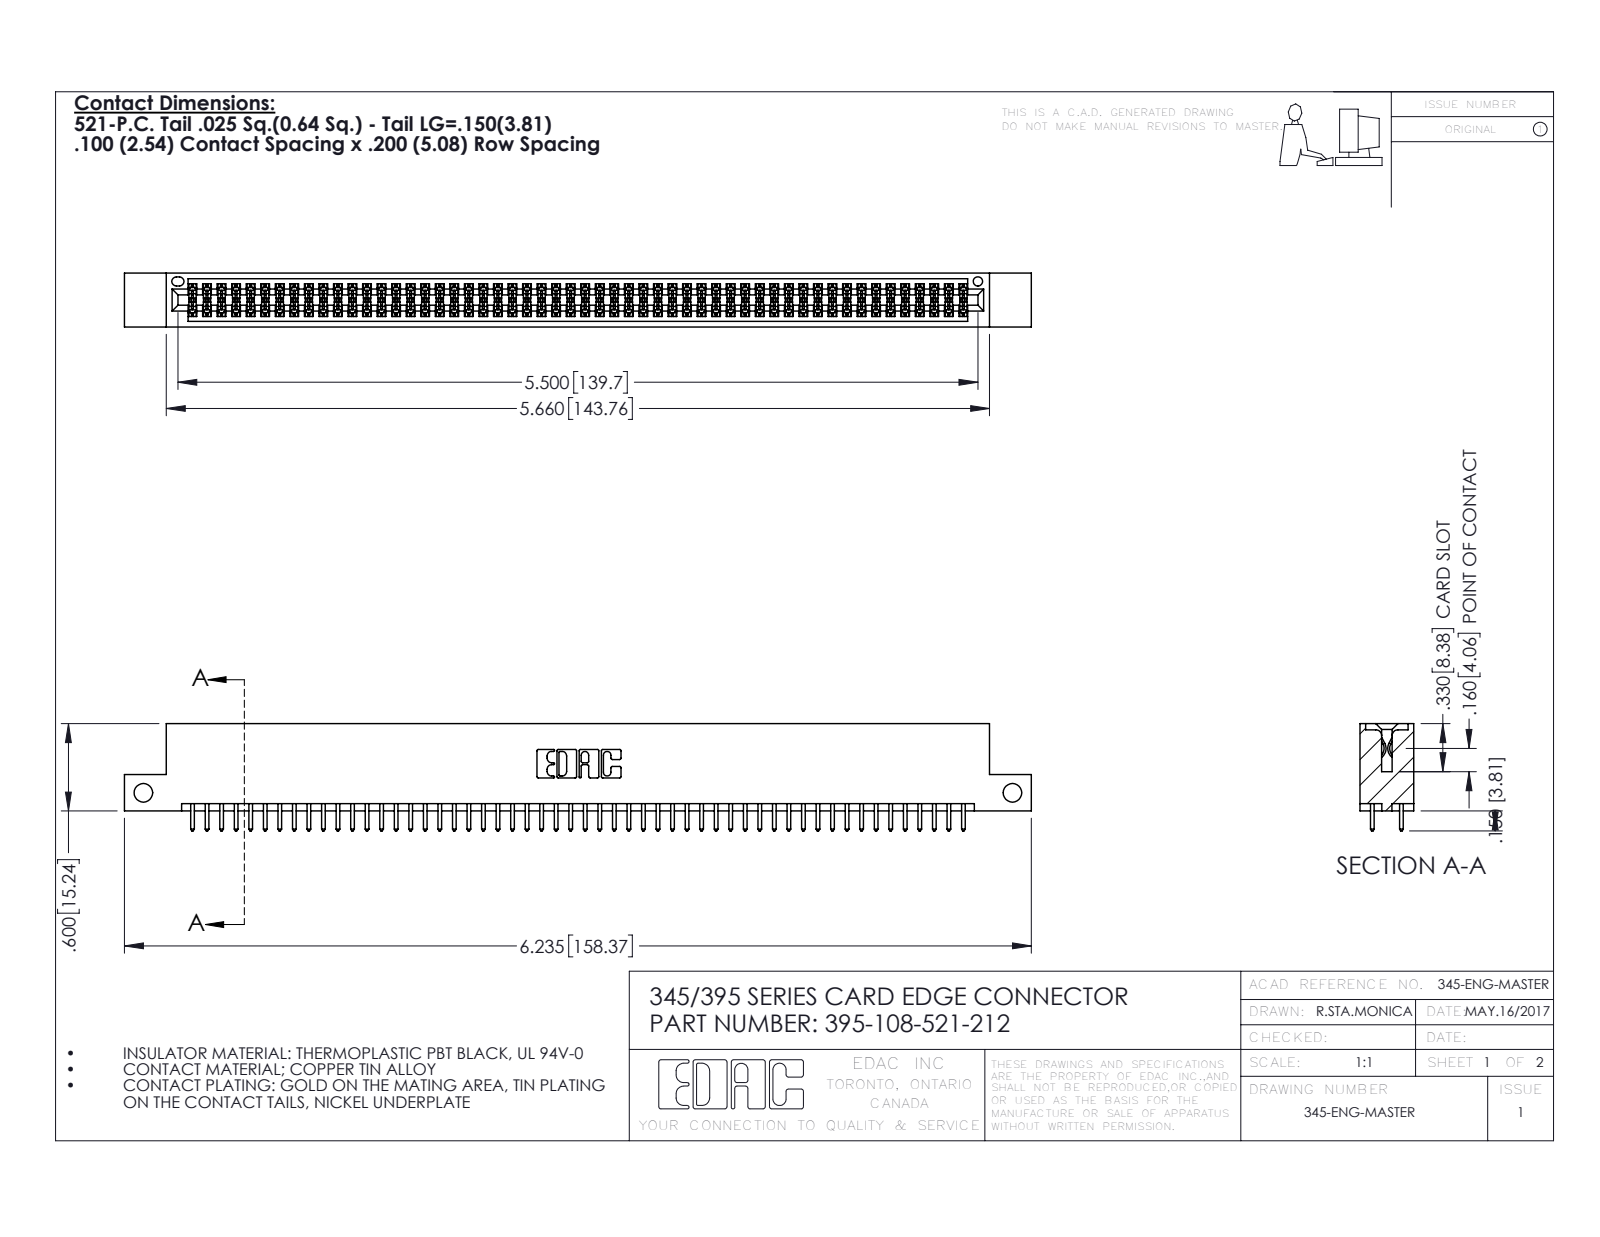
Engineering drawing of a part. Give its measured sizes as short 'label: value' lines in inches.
name: 345-292-001_345-293-121; 345 Part_Flush Mounting Lugs - Side Mount; 395-108-521-212
written by: SolidWorks 2016 (CONFIG_CONTROL_DESIGN)
unit: in
bodies: 109 solids, 5526 faces (3644 planar, 1882 cylindrical, 0 other)
size: 6.235 × 0.737 × 0.37
volume: 0.938 in³; area: 34.91 in²
holes: 2× ⌀0.128, 1× ⌀0.064
rounds: 162× R0.006, 108× R0.01, 22× R0.01, 6× R0.007, 6× R0.031, 3× R0.026, 2× R0.014, 2× R0.019
face distances: 0.298, 0.072, 0.2, 0.098, 0.272, 0.025, 0.37, 0.225, 0.175, 0.149
hole spacings: 5.975
